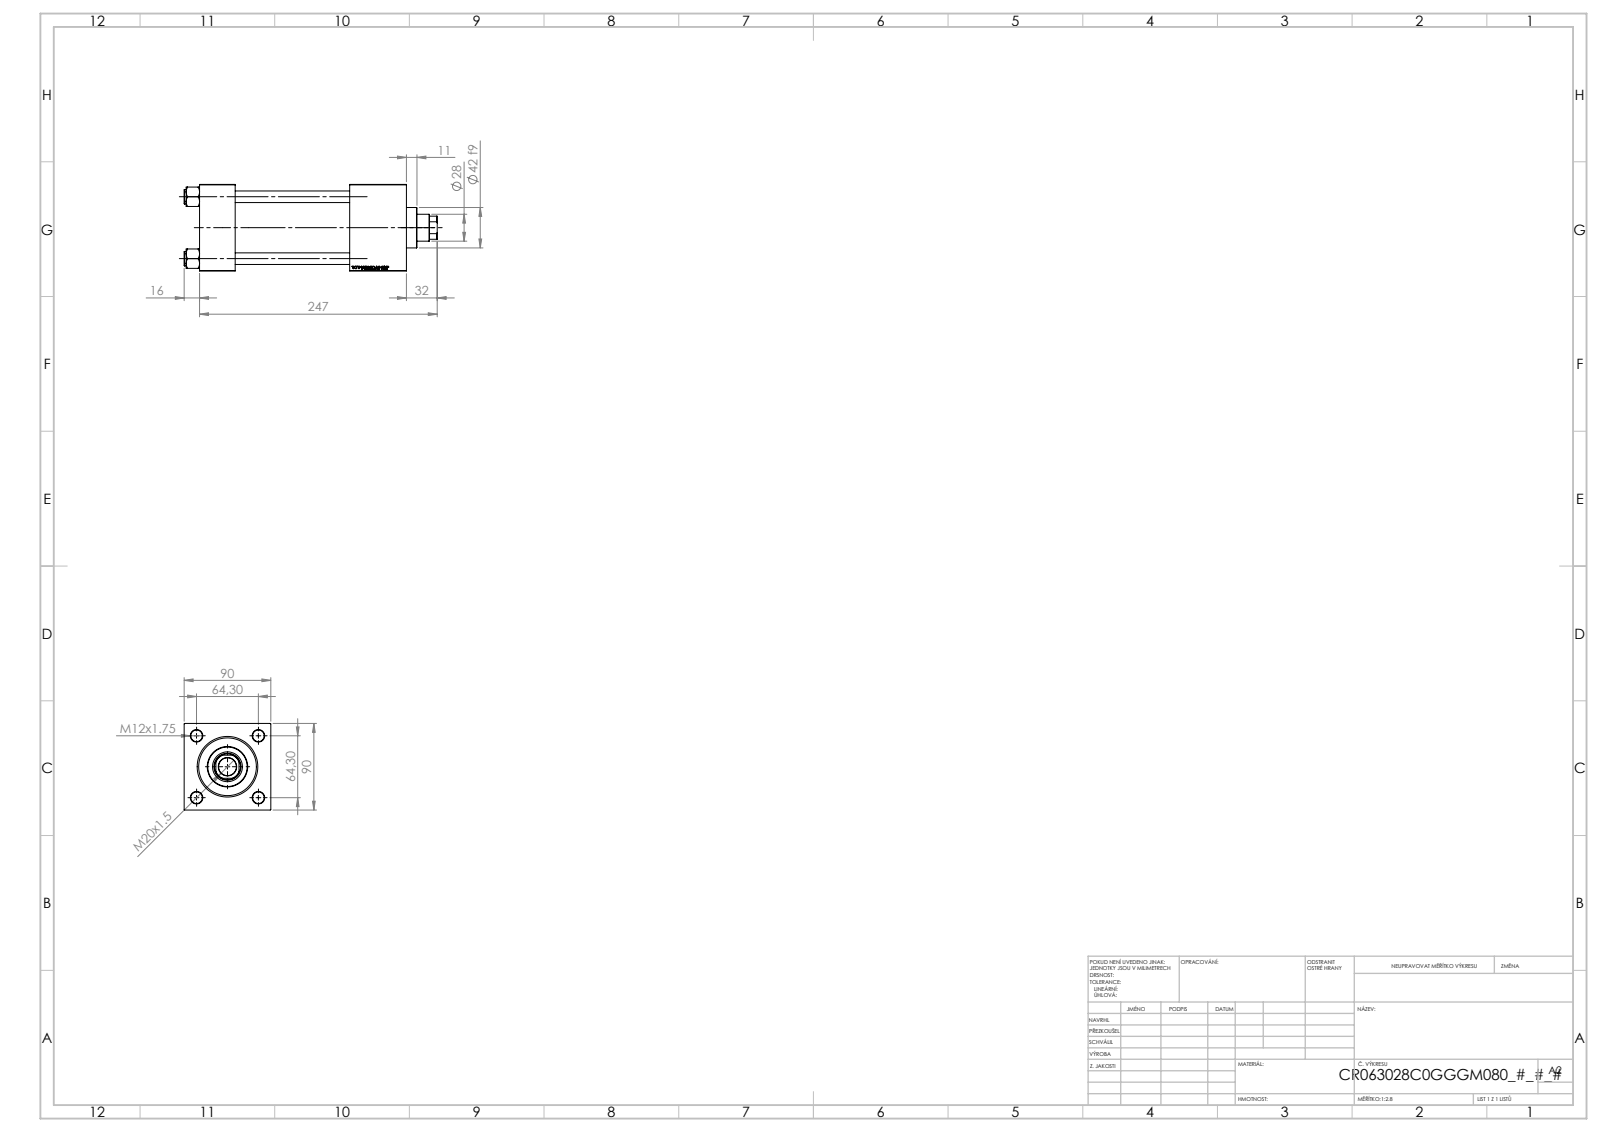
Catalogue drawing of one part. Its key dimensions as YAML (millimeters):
part_name: "V215CR_C_TYCINKA; V215_VC_A; V215CR_VCP_C; V215CR_C_Body (+1 more)"
step_written_by: "SolidWorks 2019 (CONFIG_CONTROL_DESIGN)"
units: millimeters
bodies: {solids: 11, faces: 1149, planar: 526, cylindrical: 87, other: 536}
overall_size: [263, 90, 90]
volume: 1048000
surface_area: 218341
round_holes:
  - {diameter: 12, count: 4}
  - {diameter: 7, count: 2}
  - {diameter: 20.96, count: 2}
  - {diameter: 30, count: 2}
  - {diameter: 18.5, count: 1}
  - {diameter: 28, count: 1}
  - {diameter: 31, count: 1}
  - {diameter: 50, count: 1}
  - {diameter: 60, count: 1}
  - {diameter: 63, count: 1}
round_bosses_or_shafts:
  - {diameter: 15, count: 4}
  - {diameter: 69, count: 1}
  - {diameter: 42, count: 1}
partial_cylinders:
  - {radius: 13.5, count: 1}
face_to_face_distances: [90, 37, 215, 178, 156, 119, 59, 186.3, 149.3, 30.3]
hole_center_spacings: [45.47, 64.3, 90.93, 157.5]
